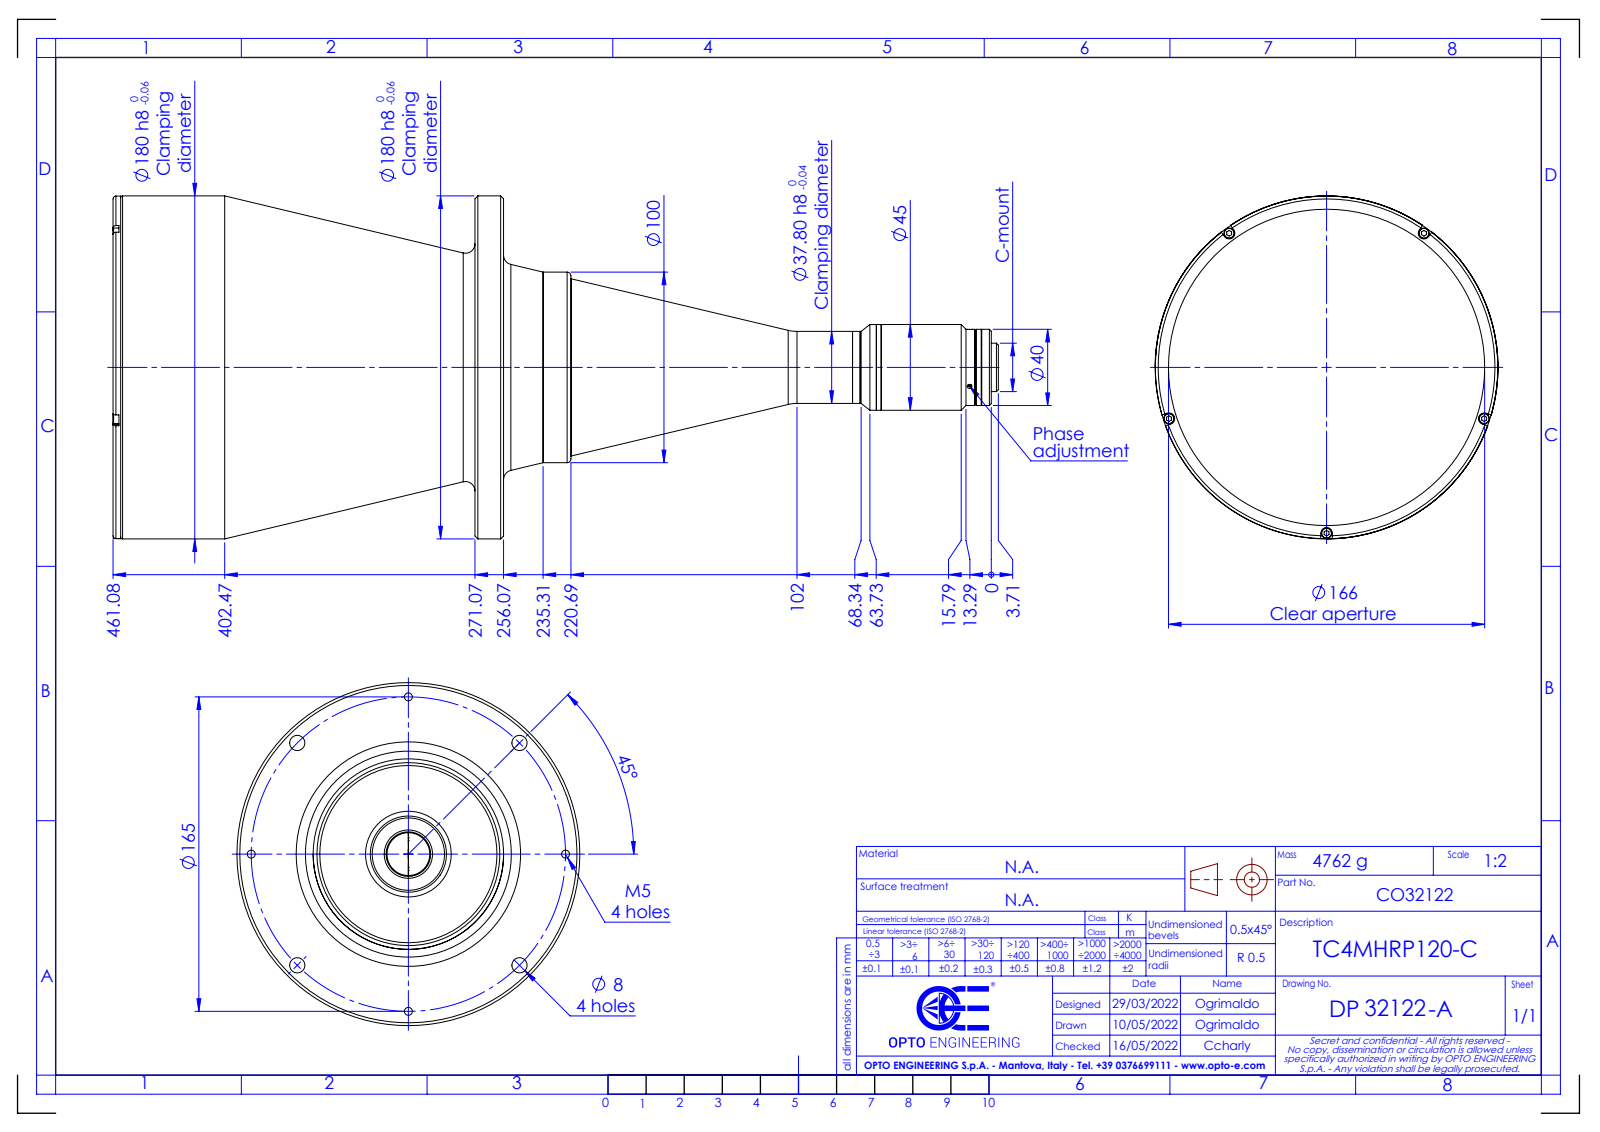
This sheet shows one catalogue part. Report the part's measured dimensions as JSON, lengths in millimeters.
{"part_name": "DP32122-A_TC4MHRP120-C", "step_written_by": "SolidWorks 2021 (CONFIG_CONTROL_DESIGN)", "units": "millimeters", "bodies": {"solids": 0, "faces": 188, "planar": 55, "cylindrical": 74, "other": 59}, "overall_size": [464.78, 180, 180], "round_holes": [[4.2, 4], [8, 4], [2.5, 3], [22.5, 1], [166, 1], [170.8, 1]], "round_bosses_or_shafts": [[5.5, 5], [180, 1], [179.8, 1], [100, 1], [93, 1], [45, 1], [40, 1], [37.8, 1]], "partial_cylinders_radius": [[3, 4]], "face_to_face_distances": [15, 190.01, 205.01, 4, 186.01, 201.01, 456.07, 452.07, 266.06, 251.06], "hole_center_spacings": [63.14, 152.44, 82.5, 82.51, 116.67, 116.68, 165, 165.01]}
